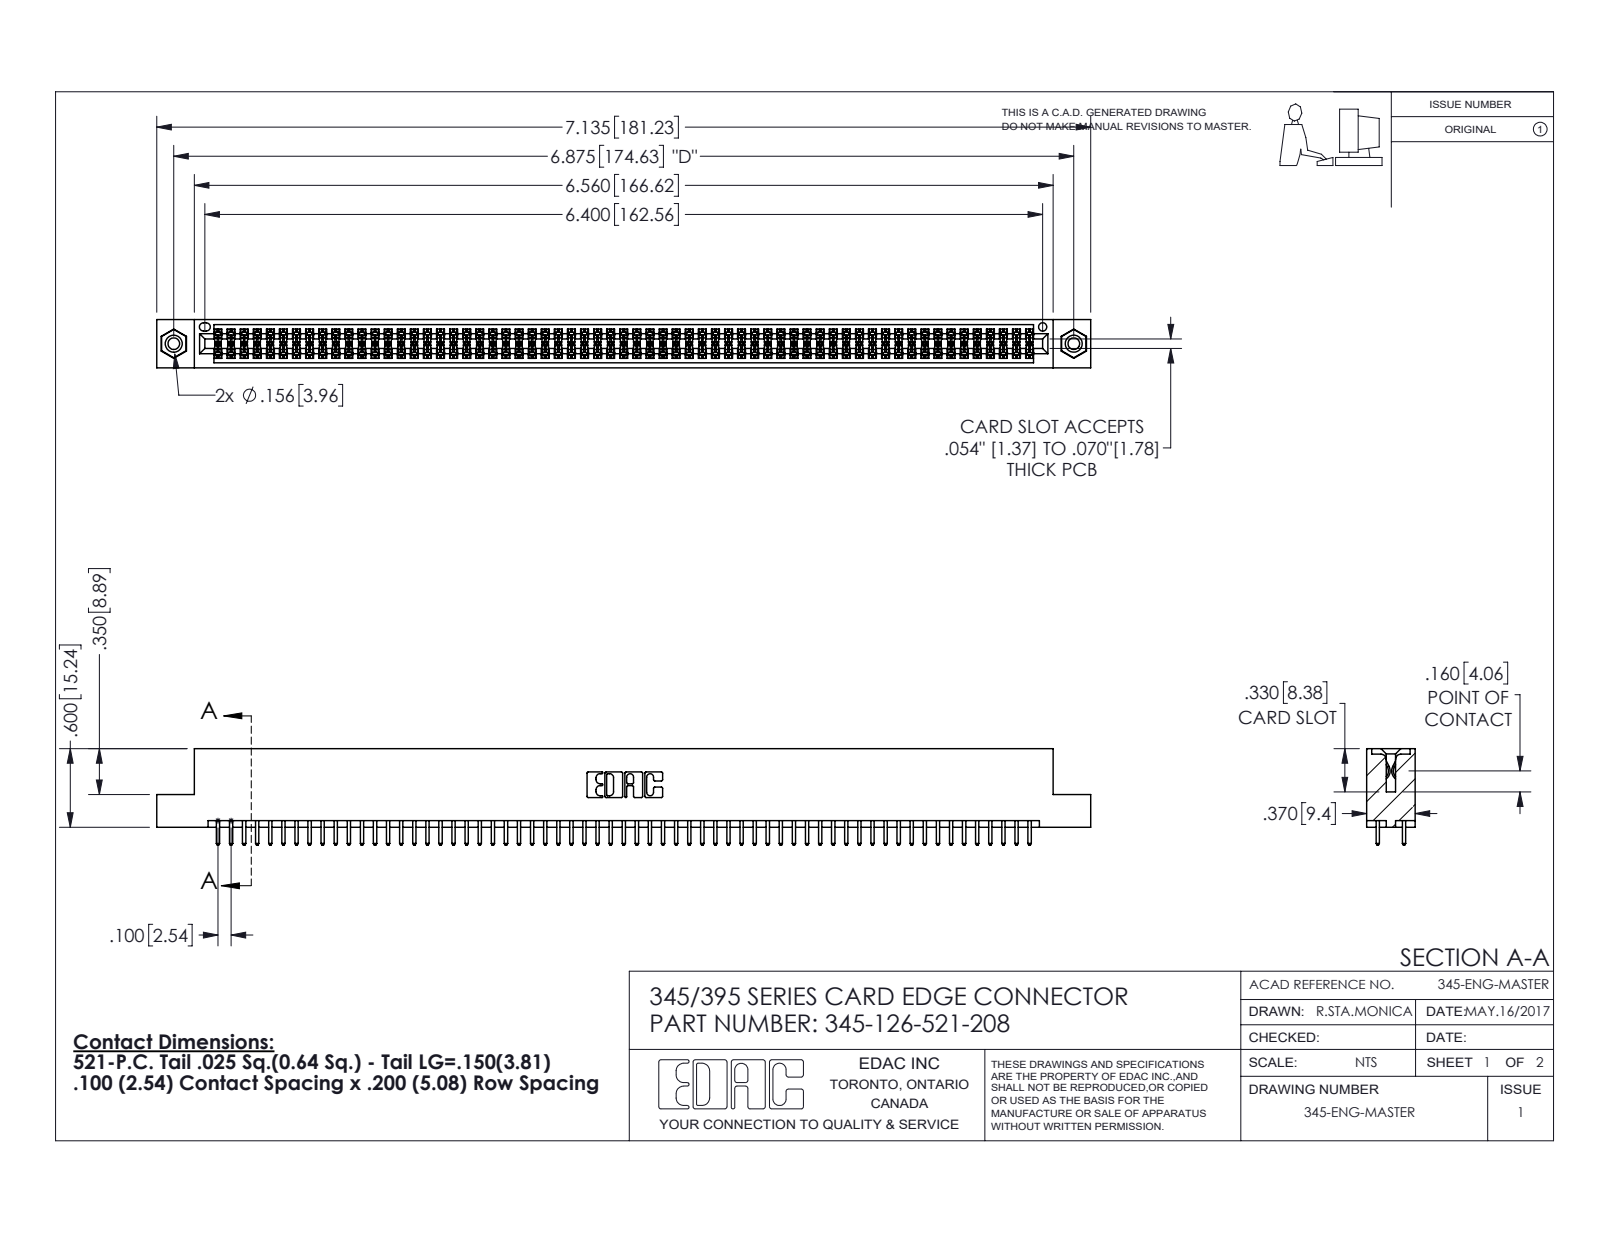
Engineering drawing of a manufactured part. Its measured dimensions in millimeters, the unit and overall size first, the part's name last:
Units: millimetres
Overall size (bounding box): 181.2 × 18.7 × 9.4
Round holes (diameter × count): ⌀2.3 ×2, ⌀3.2 ×2, ⌀4 ×2, ⌀1.6 ×1
Round bosses / shafts (diameter × count): ⌀3.9 ×2
Partial cylindrical surfaces — rounded edges, fillets, slot ends (radius × count): R0.2 ×189, R0.3 ×126, R0.3 ×22, R0.2 ×6, R0.8 ×6, R0.7 ×3, R0.4 ×2, R0.5 ×2
Main face-to-face distances: 1.8, 7.6, 5.1, 2.5, 6.9, 0.6, 9.4, 5.7, 4.4, 3.8
Hole centre spacings: 6.9, 168.6, 174.6
Volume: 17 750 mm³ · Surface area: 26 310 mm²
Bodies: 129 solids, 6486 faces (4270 planar, 2200 cylindrical, 16 other)
Part name (STEP PRODUCT): 345-292-001_345-293-121; 345 Part_Flush Mounting Lugs - 0.156 Dia-TI; 345-250-001_345-250-003-102; 345-126-521-208
STEP written by: SolidWorks 2016 (CONFIG_CONTROL_DESIGN)
